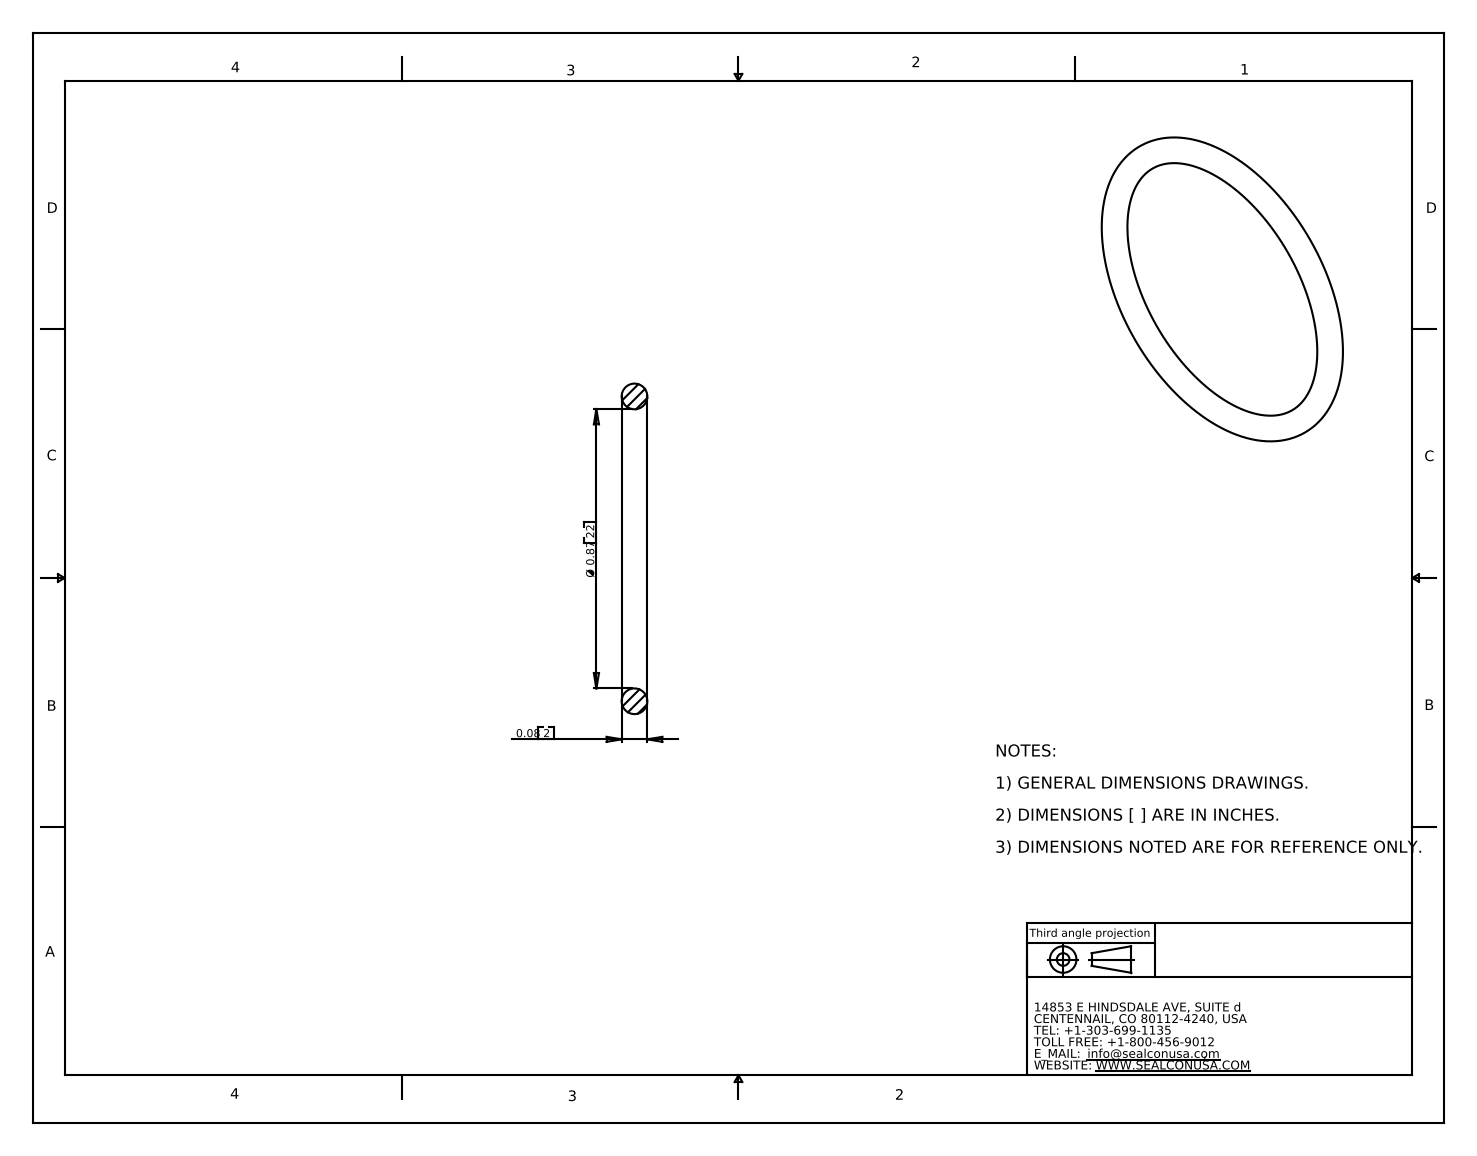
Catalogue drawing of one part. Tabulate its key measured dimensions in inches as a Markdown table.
| quantity | value |
| --- | --- |
| part name | OM-25-VT |
| STEP written by | SolidWorks 2007 (CONFIG_CONTROL_DESIGN) |
| units | inches |
| bodies | 1 solid, 4 faces (0 planar, 0 cylindrical, 4 other) |
| overall size | 1.03 × 1.03 × 0.08 |
| volume | 0.015 in³ |
| surface area | 0.75 in² |
